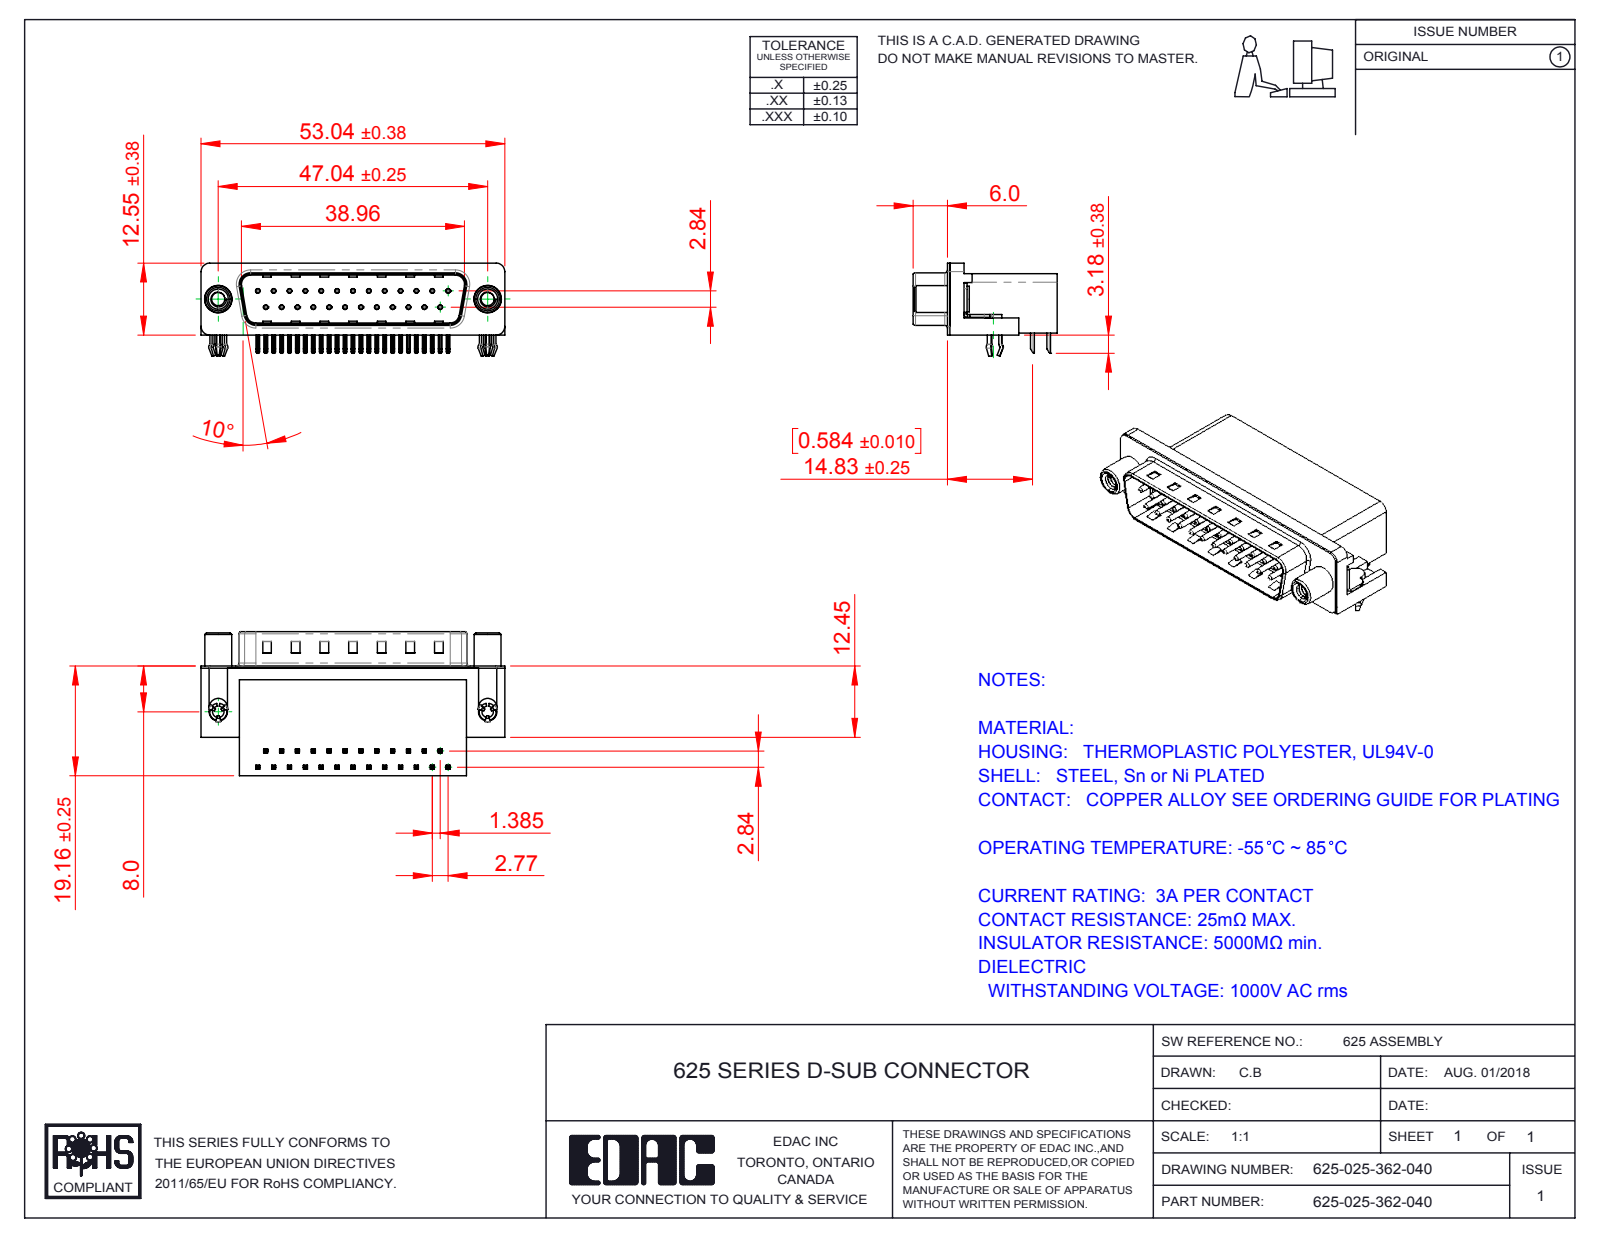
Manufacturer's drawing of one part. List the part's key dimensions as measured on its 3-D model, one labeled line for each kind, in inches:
Part name (STEP PRODUCT): 625 3 Prong Board Lock; 625 Contact Top; 625 Housing_25 Socket; 625 Round Threaded Standoff (+3 more)
STEP written by: SolidWorks 2016 (CONFIG_CONTROL_DESIGN)
Units: inches
Bodies: 31 solids, 2363 faces (1435 planar, 675 cylindrical, 253 other)
Overall size (bounding box): 2.088 × 0.991 × 0.64
Volume: 0.565 in³ · Surface area: 14.14 in²
Round holes (diameter × count): ⌀0.014 ×25, ⌀0.031 ×25, ⌀0.079 ×2, ⌀0.091 ×2, ⌀0.122 ×2, ⌀0.157 ×2, ⌀0.189 ×2, ⌀0.197 ×2
Round bosses / shafts (diameter × count): ⌀0.03 ×25, ⌀0.193 ×2, ⌀0.185 ×2, ⌀0.177 ×2, ⌀0.152 ×2, ⌀0.118 ×2
Partial cylindrical surfaces — rounded edges, fillets, slot ends (radius × count): R0.01 ×104, R0.005 ×50, R0.039 ×16, R0.02 ×9, R0.063 ×8, R0.059 ×7, R0.035 ×4, R0.079 ×4
Main face-to-face distances: 0.016, 0.407, 0.739, 0.083, 0.345, 0.412, 0.428, 0.067, 0.754, 0.114
Hole centre spacings: 0.124, 0.109, 0.436, 0.218, 0.327, 0.198, 0.545, 0.294
